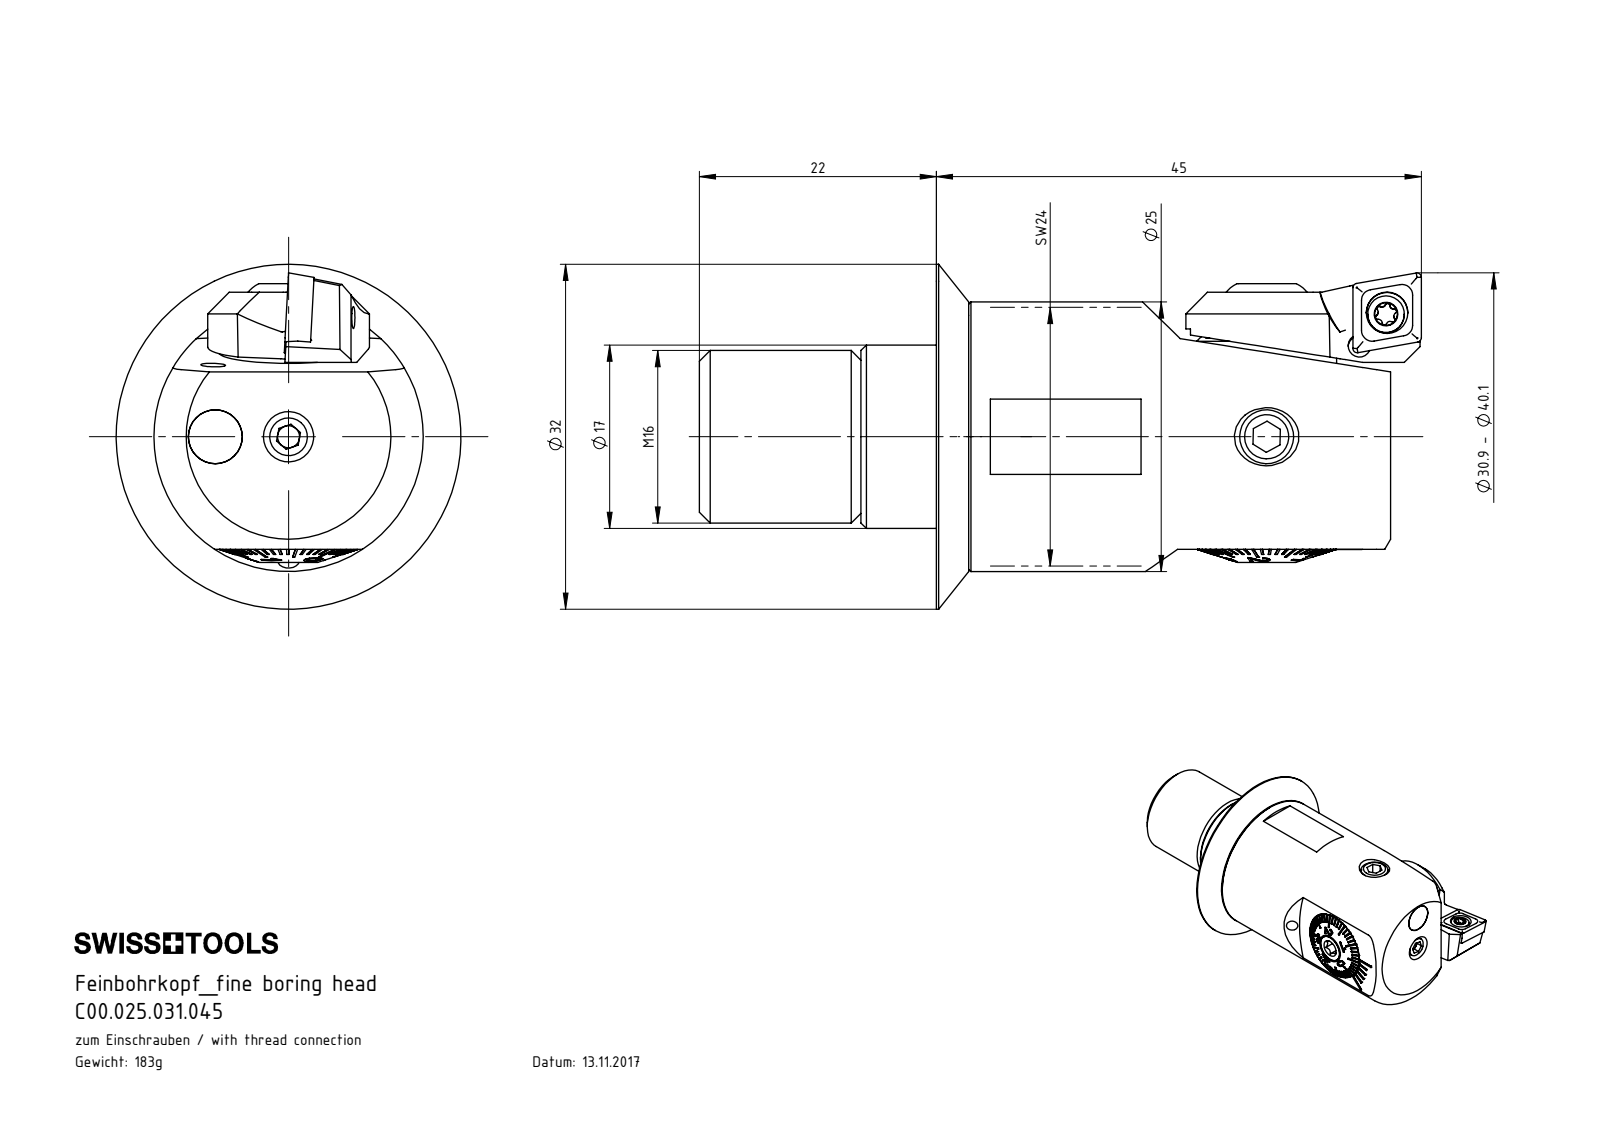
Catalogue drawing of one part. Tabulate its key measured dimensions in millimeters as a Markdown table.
| quantity | value |
| --- | --- |
| part name | F25-BG2.010.011_A; F25-WCA.001.006; F25-BG1.002.013_C; WCA-ER2.001.006_A (+8 more) |
| STEP written by | SolidWorks 2017 (CONFIG_CONTROL_DESIGN) |
| units | millimeters |
| bodies | 20 solids, 834 faces (366 planar, 154 cylindrical, 314 other) |
| overall size | 67 × 32 × 32 |
| volume | 23 344 mm³ |
| surface area | 14 939 mm² |
| round holes (diameter × count) | 2 × 5, 2.05 × 2, 4.2 × 2, 2.1 × 1, 2.4 × 1, 2.7 × 1, 2.8 × 1, 3 × 1, 3.3 × 1, 3.85 × 1, 5 × 1, 5.5 × 1 |
| round bosses / shafts (diameter × count) | 5 × 2, 4.95 × 2, 2.5 × 2, 32 × 1, 25 × 1, 16 × 1, 12.98 × 1, 12.85 × 1 |
| partial cylindrical surfaces (radius × count) | 0.21 × 6, 0.36 × 5, 0.5 × 4, 1.32 × 2, 0.2 × 1, 0.36 × 1, 1.05 × 1, 1.25 × 1 |
| main face-to-face distances | 3, 42.15, 39.15, 8, 1.5, 15, 19.95, 3.1, 15.7, 0.8 |
| hole center spacings | 3.84, 3.99, 4.48, 6.8, 9.46, 16.65 |
